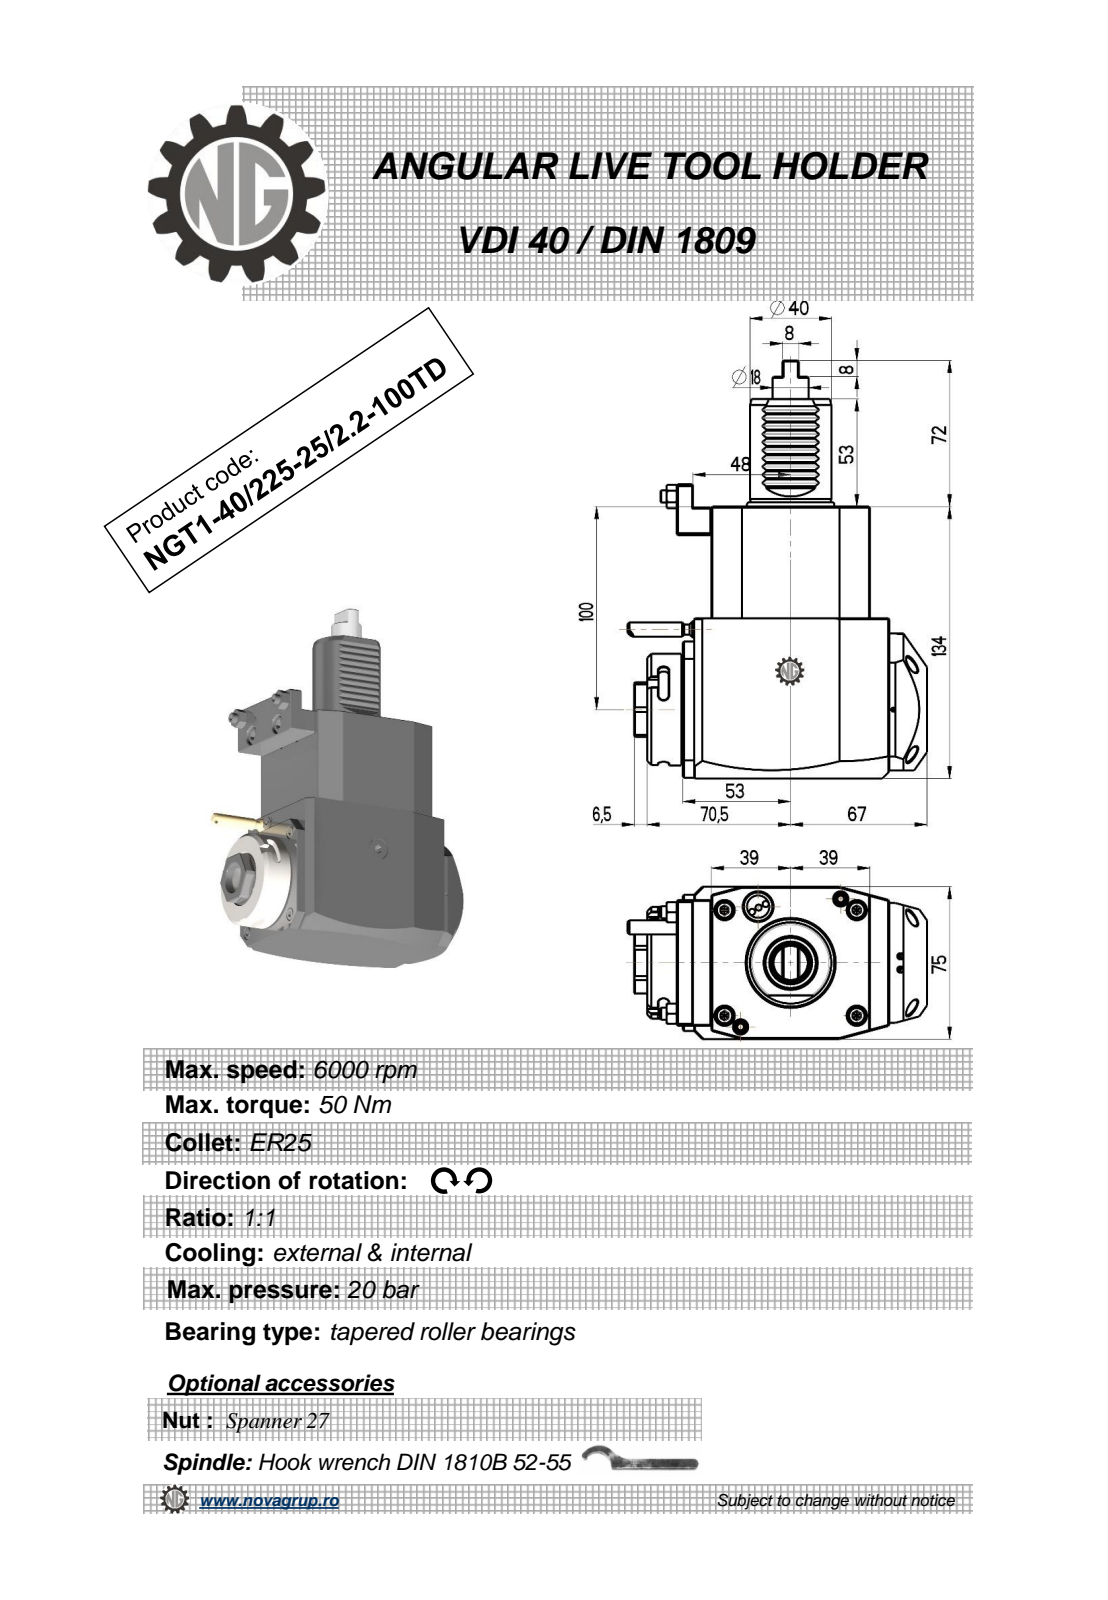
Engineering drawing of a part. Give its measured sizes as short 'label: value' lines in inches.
name: NGT1_40_225_25_1_2_100TD
written by: PRO/ENGINEER BY PARAMETRIC TECHNOLOGY CORPORATION, 2010280 (CONFIG_CONTROL_DESIGN)
unit: in
bodies: 1 solid, 332 faces (178 planar, 68 cylindrical, 86 other)
size: 8.11 × 5.8 × 2.953
volume: 65.6 in³; area: 120.1 in²
holes: 1× ⌀0.098, 1× ⌀0.118, 1× ⌀0.709
bosses: 2× ⌀0.236, 1× ⌀2.165, 1× ⌀1.89, 1× ⌀1.575, 1× ⌀0.701, 1× ⌀0.315, 1× ⌀0.276, 1× ⌀0.197
rounds: 10× R0.012, 10× R0.012, 6× R0.098, 2× R0.031, 2× R7.087, 1× R0.02, 1× R0.591, 1× R0.965
face distances: 2.953, 5.276, 0.551, 3.071, 3.622, 4.724, 0.02, 0.669, 0.689, 0.571
hole spacings: 1.701
